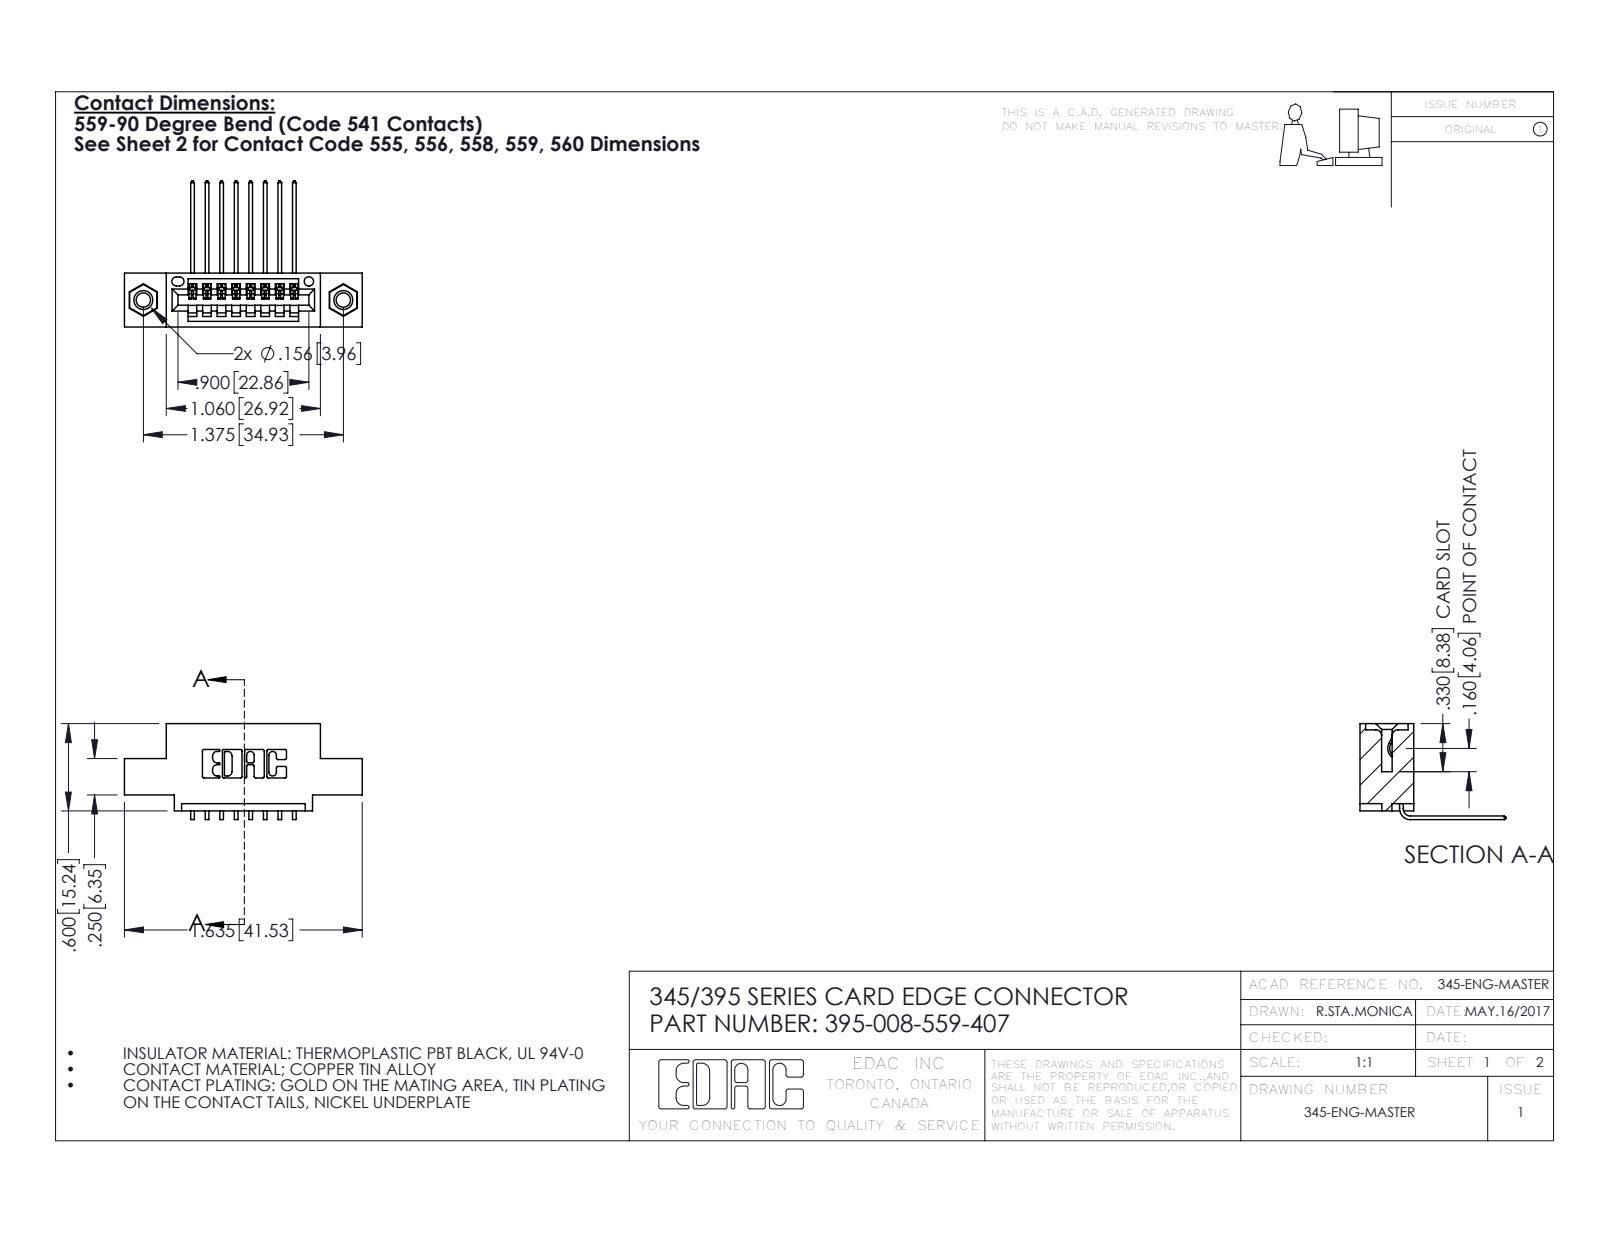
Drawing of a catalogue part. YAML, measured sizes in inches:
part_name: "395-008-559-407; 345-250-001_345-250-005-103; 345-292-001_558 559 Tail - 1; 345 Part_0.110 Offset - 0.156 Dia-TI"
step_written_by: "SolidWorks 2016 (CONFIG_CONTROL_DESIGN)"
units: inches
bodies: {solids: 11, faces: 670, planar: 452, cylindrical: 202, other: 16}
overall_size: [1.635, 1.005, 0.659]
volume: 0.22
surface_area: 7.131
round_holes:
  - {diameter: 0.098, count: 2}
  - {diameter: 0.125, count: 2}
  - {diameter: 0.156, count: 2}
  - {diameter: 0.064, count: 1}
round_bosses_or_shafts:
  - {diameter: 0.155, count: 2}
partial_cylinders:
  - {radius: 0.01, count: 22}
  - {radius: 0.006, count: 16}
  - {radius: 0.007, count: 6}
  - {radius: 0.031, count: 6}
  - {radius: 0.026, count: 3}
  - {radius: 0.031, count: 2}
  - {radius: 0.04, count: 2}
  - {radius: 0.014, count: 1}
face_to_face_distances: [0.2, 0.37, 0.1, 0.072, 0.298, 0.3, 0.16, 0.06, 0.4, 0.04]
hole_center_spacings: [0.27, 1.144, 1.375]
